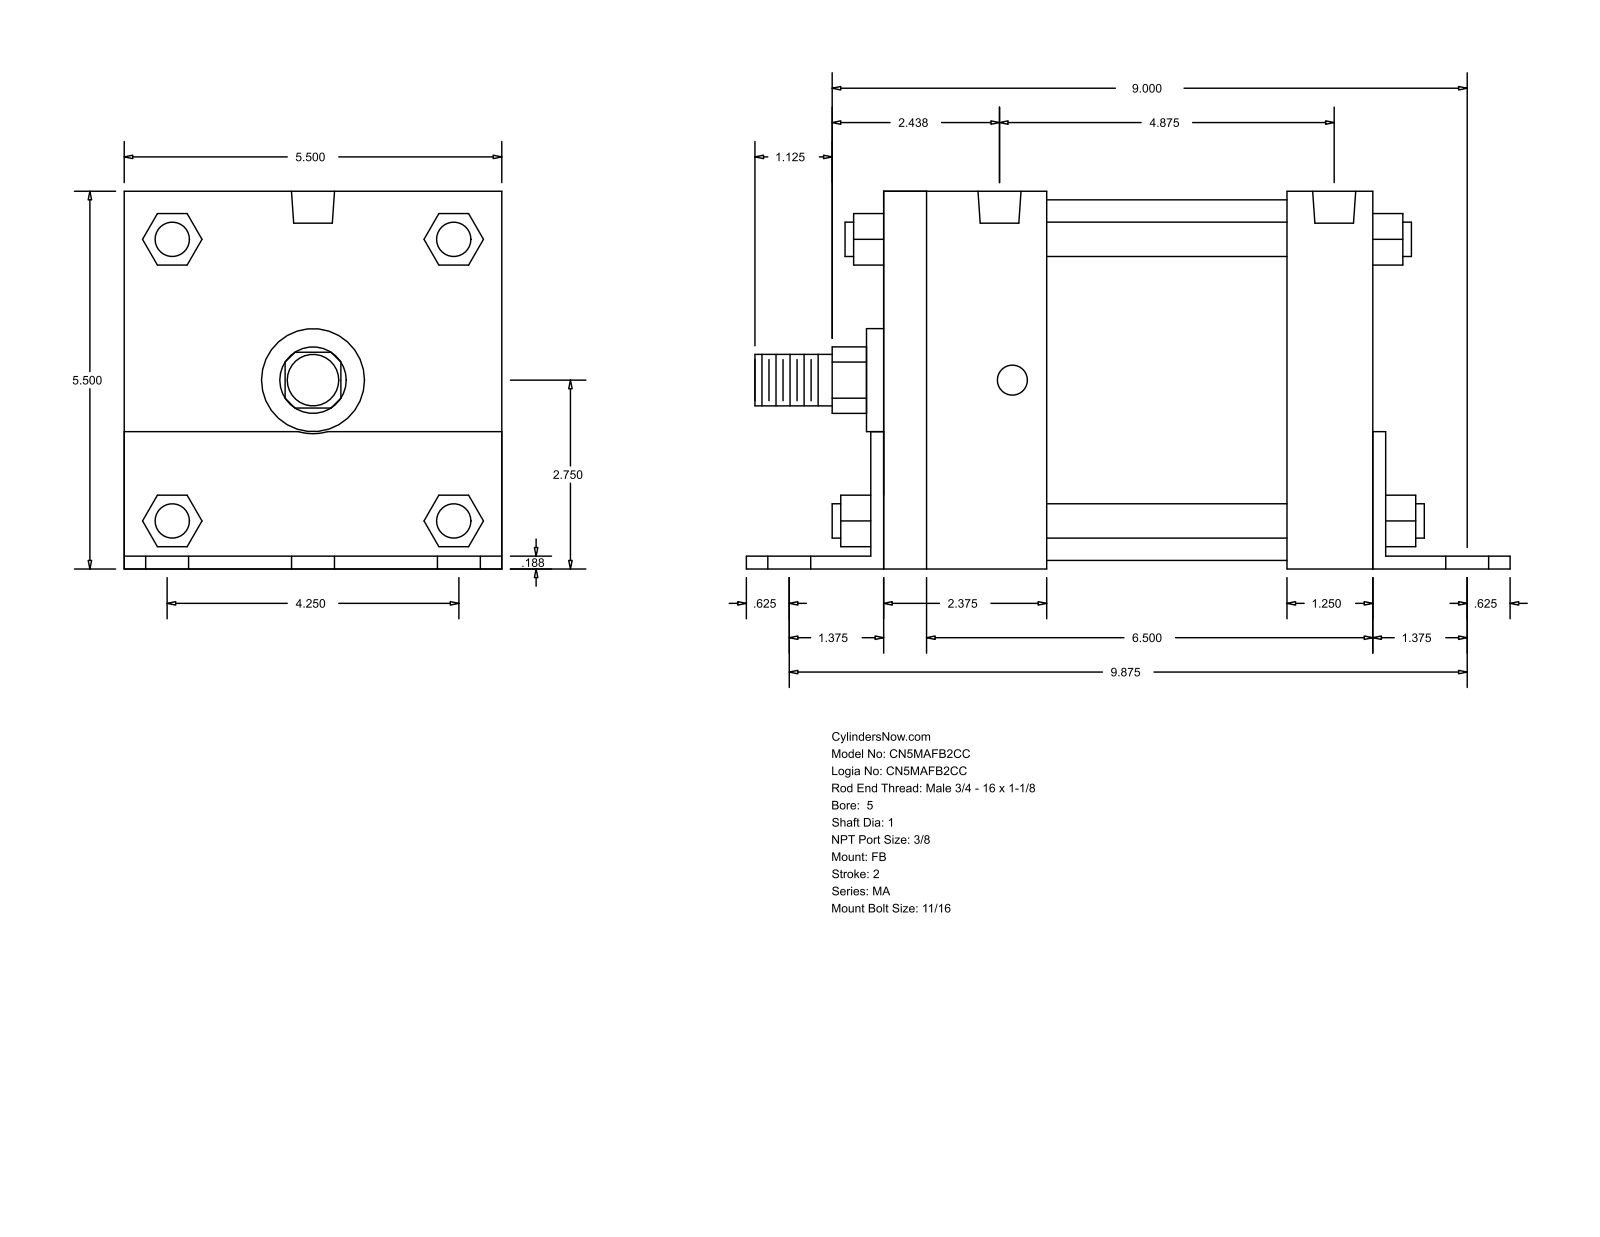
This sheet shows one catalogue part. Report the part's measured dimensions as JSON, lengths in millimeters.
{"part_name": "MA_FB__0500_1", "step_written_by": "GSSL Pune (CONFIG_CONTROL_DESIGN)", "units": "millimeters", "bodies": {"solids": 0, "faces": 140, "planar": 105, "cylindrical": 35, "other": 0}, "overall_size": [282.57, 139.75, 139.7], "round_holes": [[17.46, 6], [11.11, 4], [15.93, 2]], "round_bosses_or_shafts": [[12.7, 4], [133.35, 1], [38.1, 1], [25.4, 1], [19.05, 1]], "partial_cylinders_radius": [[12.29, 1], [19.81, 1]], "face_to_face_distances": [139.7, 4.76, 139.75, 185.74, 4.71, 134.99, 180.98, 190.5, 36.51, 31.75], "hole_center_spacings": [53.98, 256.57, 250.83, 73.04, 76.34, 94.68, 98.63, 107.96]}
